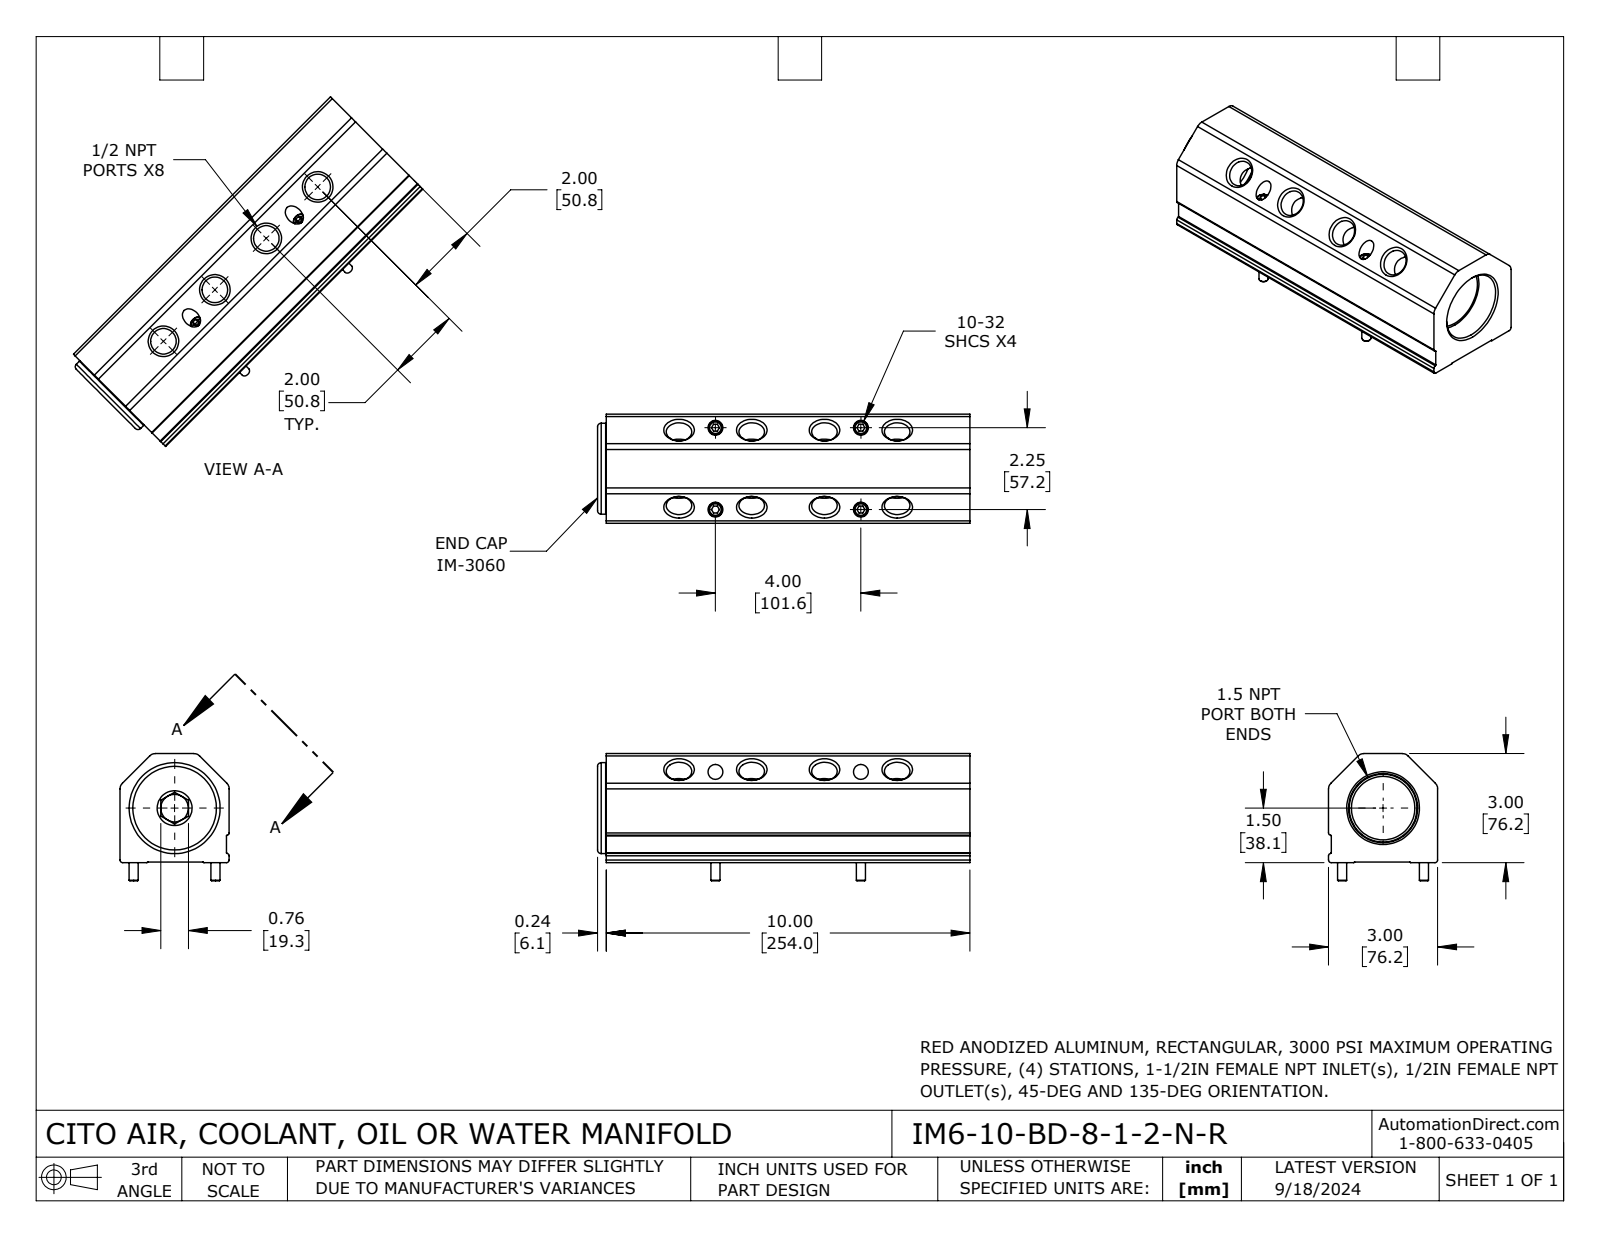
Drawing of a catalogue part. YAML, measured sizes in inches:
part_name: "IM6-10-BD-8-1-2-N-R"
step_written_by: "SolidWorks 2023 (CONFIG_CONTROL_DESIGN)"
units: inches
bodies: {solids: 6, faces: 210, planar: 76, cylindrical: 74, other: 60}
overall_size: [10.24, 3.5, 3]
volume: 57.12
surface_area: 216.9
round_holes:
  - {diameter: 0.703, count: 8}
  - {diameter: 0.266, count: 4}
  - {diameter: 0.406, count: 4}
  - {diameter: 0.758, count: 1}
  - {diameter: 1.743, count: 1}
  - {diameter: 2.262, count: 1}
round_bosses_or_shafts:
  - {diameter: 0.375, count: 4}
  - {diameter: 0.25, count: 4}
  - {diameter: 2.5, count: 1}
  - {diameter: 1.984, count: 1}
  - {diameter: 1.761, count: 1}
partial_cylinders:
  - {radius: 0.02, count: 6}
  - {radius: 0.225, count: 4}
  - {radius: 0.062, count: 2}
  - {radius: 0.075, count: 2}
face_to_face_distances: [3, 0.02, 2.98, 10, 0.075, 2.925, 0.24, 10.24, 0.764, 0.524]
hole_center_spacings: [2, 4, 2.25, 4.589, 6]
